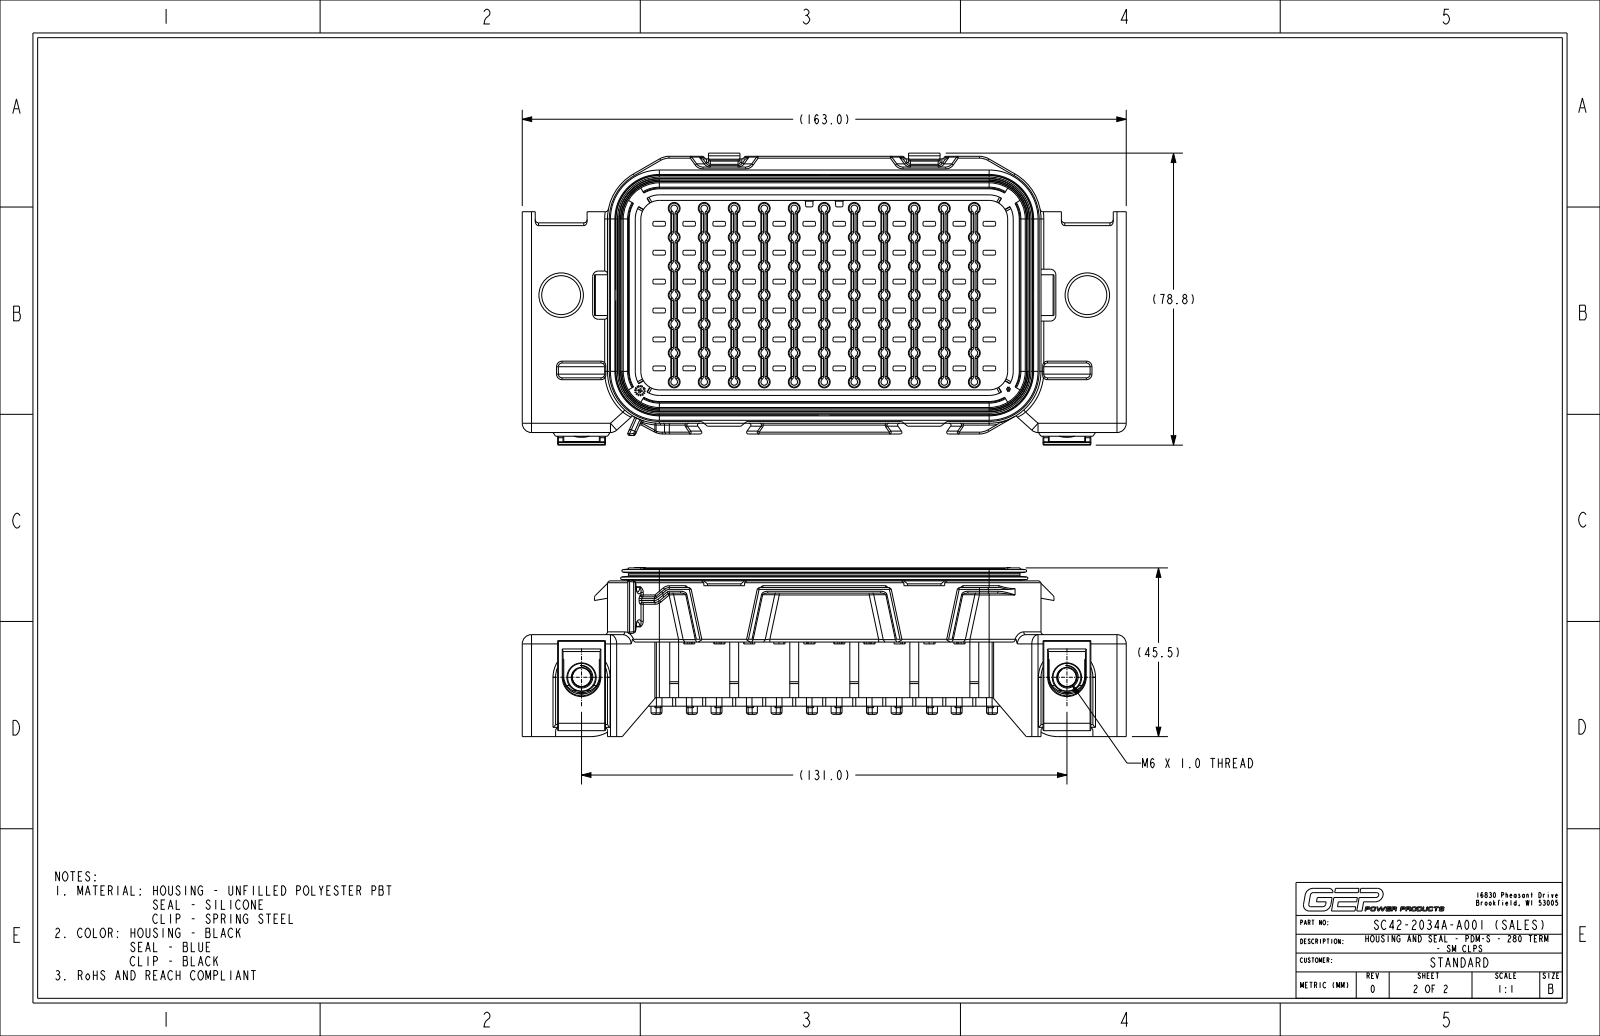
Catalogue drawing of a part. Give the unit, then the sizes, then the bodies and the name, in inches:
Units: inches
Overall size (bounding box): 6.417 × 3.1 × 1.795
Round holes (diameter × count): ⌀0.264 ×72, ⌀0.413 ×4, ⌀0.197 ×2, ⌀0.295 ×2, ⌀0.492 ×2
Round bosses / shafts (diameter × count): ⌀0.276 ×2, ⌀0.157 ×1
Partial cylindrical surfaces — rounded edges, fillets, slot ends (radius × count): R0.02 ×725, R0.016 ×350, R0.055 ×77, R0.175 ×72, R0.008 ×52, R0.012 ×52, R0.035 ×43, R0.039 ×40
Main face-to-face distances: 0.079, 0.217, 0.295, 0.354, 0.059, 0.453, 0.276, 0.374, 0.098, 0.071
Hole centre spacings: 0.692, 0.319, 0.885, 0.638, 0.614, 1.137, 1.416, 0.957
Volume: 10.57 in³ · Surface area: 175.3 in²
Bodies: 1 solid, 8128 faces (2274 planar, 2310 cylindrical, 3544 other)
Part name (STEP PRODUCT): SC42-2034A-A001_NCF_SW0001
STEP written by: CREO PARAMETRIC BY PTC INC, 2024014 (CONFIG_CONTROL_DESIGN)
